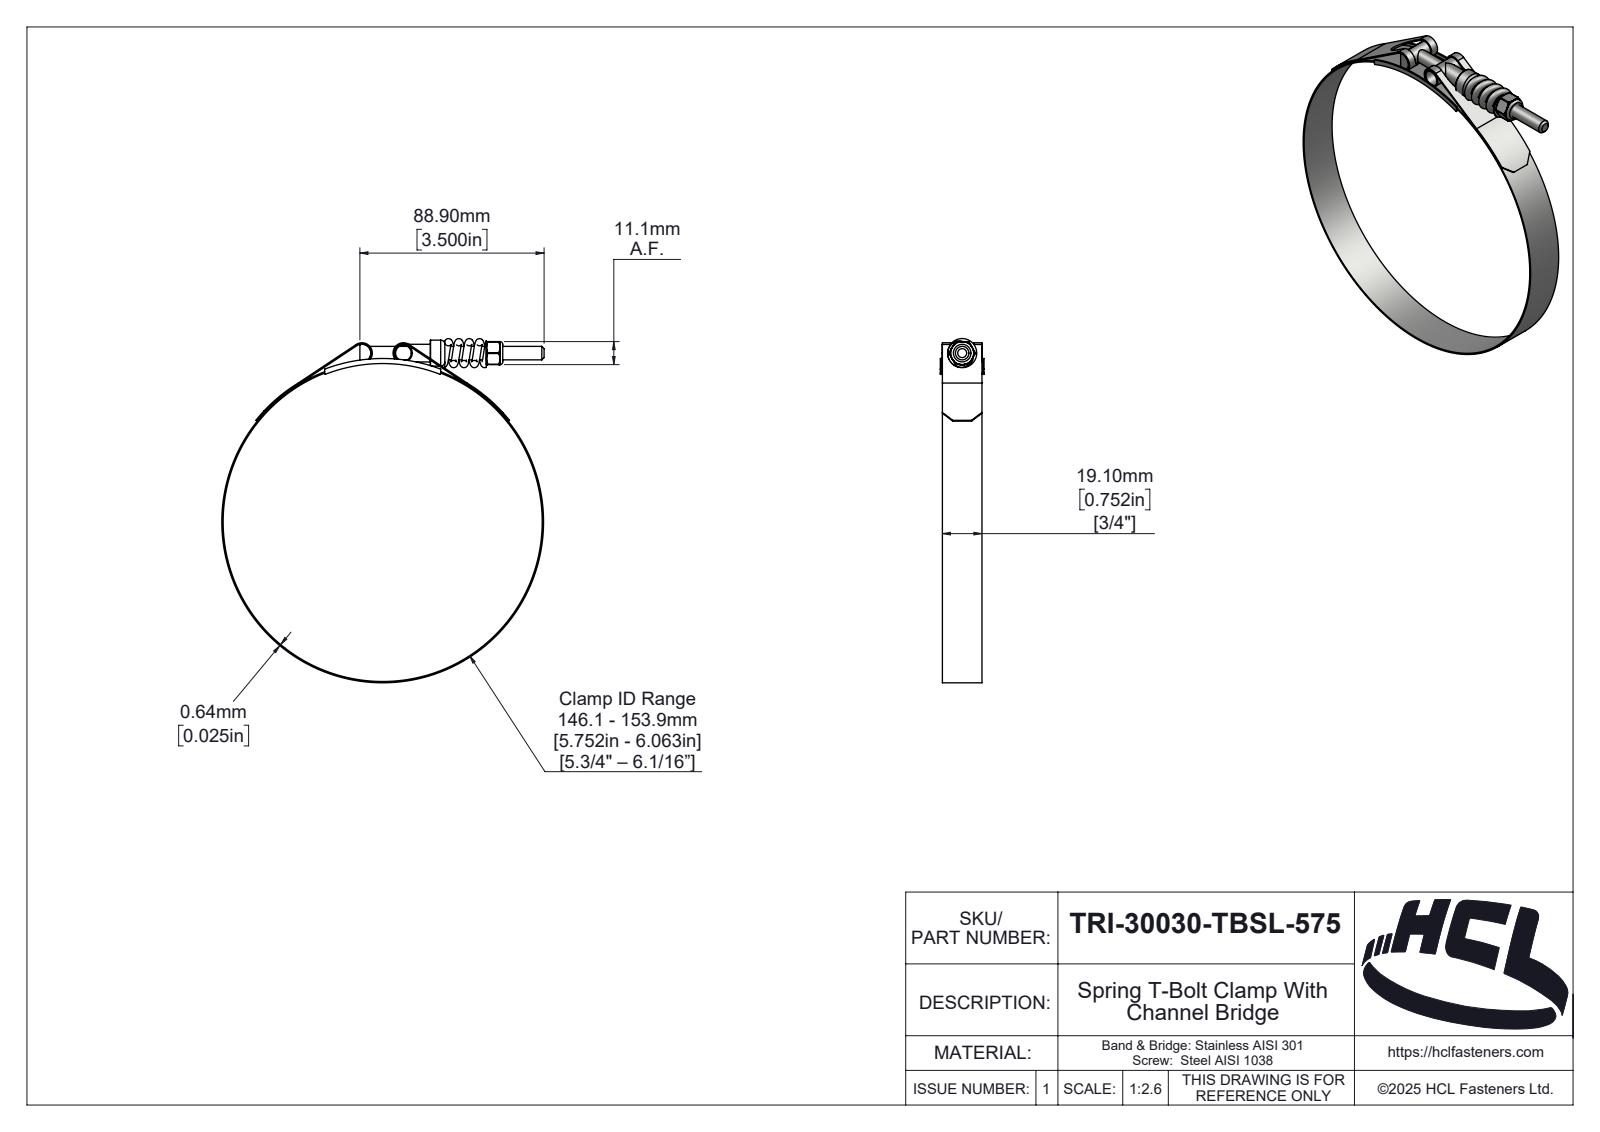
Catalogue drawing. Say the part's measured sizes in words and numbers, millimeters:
The part is named "TRI-30030-TBSL-575". Its 3-D file was written by "SolidWorks 2025 (AUTOMOTIVE_DESIGN)". It is 7 solids with 332 faces: 48 planar, 122 cylindrical and 162 other. Overall it measures 166.05 by 156.54 by 21.1 millimeters. Its volume is 14 543 cubic millimeters and its surface area 32 919 square millimeters. Round holes: 1 of diameter 5.4, 1 of diameter 6.35, 1 of diameter 6.5, 1 of diameter 7.52, 1 of diameter 154. Round bosses or shafts: 2 of diameter 8.52, 1 of diameter 155.28, 1 of diameter 12.52. Partial cylindrical surfaces (rounded edges, fillets, slot ends): 6 of radius 0.39, 2 of radius 0.5, 2 of radius 4.36, 2 of radius 5, 1 of radius 0.59, 1 of radius 2.42, 1 of radius 3.03, 1 of radius 3.19. The main face-to-face distances are 0.64, 19.1, 1, 20.1, 20.46, 0.36, 19.46, 21.1, 61, 11.11. The hole center spacings are 82.
